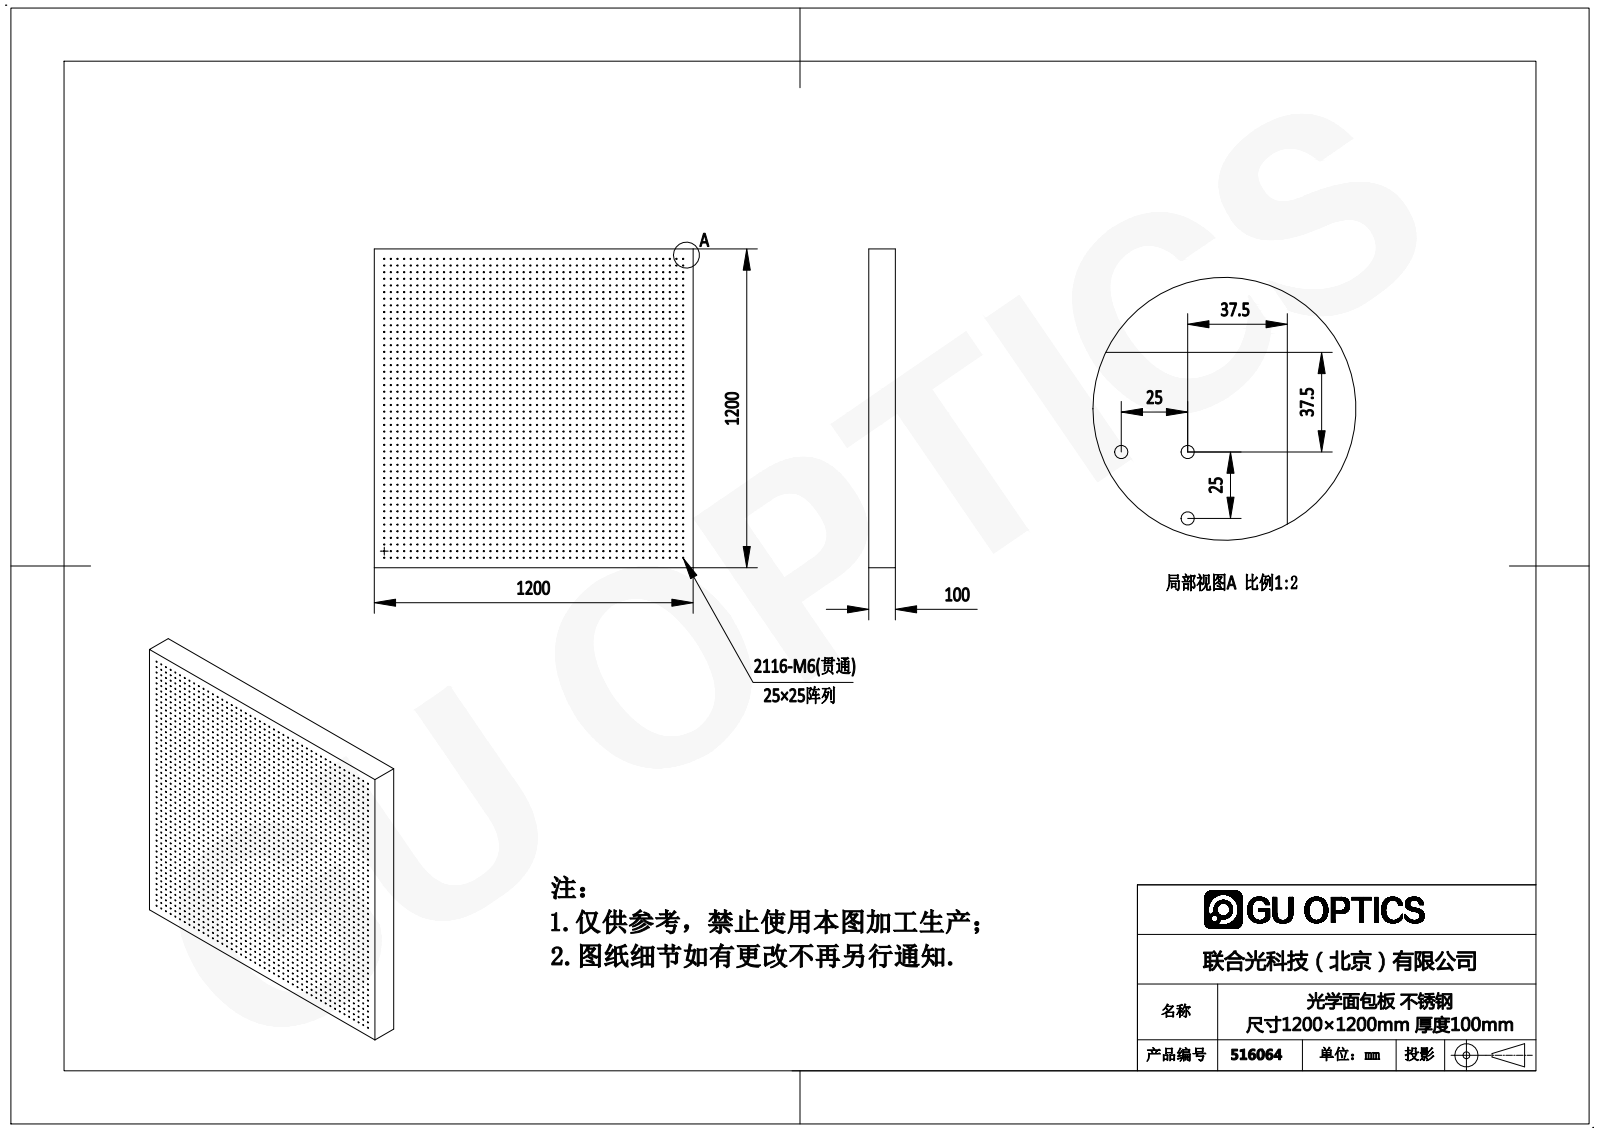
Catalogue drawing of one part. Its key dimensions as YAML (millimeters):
part_name: "516064"
step_written_by: "SolidWorks 2016 (AUTOMOTIVE_DESIGN)"
units: millimeters
bodies: {solids: 1, faces: 4238, planar: 6, cylindrical: 4232, other: 0}
overall_size: [1200, 1200, 100]
volume: 139800000
surface_area: 6601000
round_holes:
  - {diameter: 5, count: 2116}
face_to_face_distances: [100, 1200]
hole_center_spacings: [25, 50, 75, 100, 125, 150, 175, 200]
